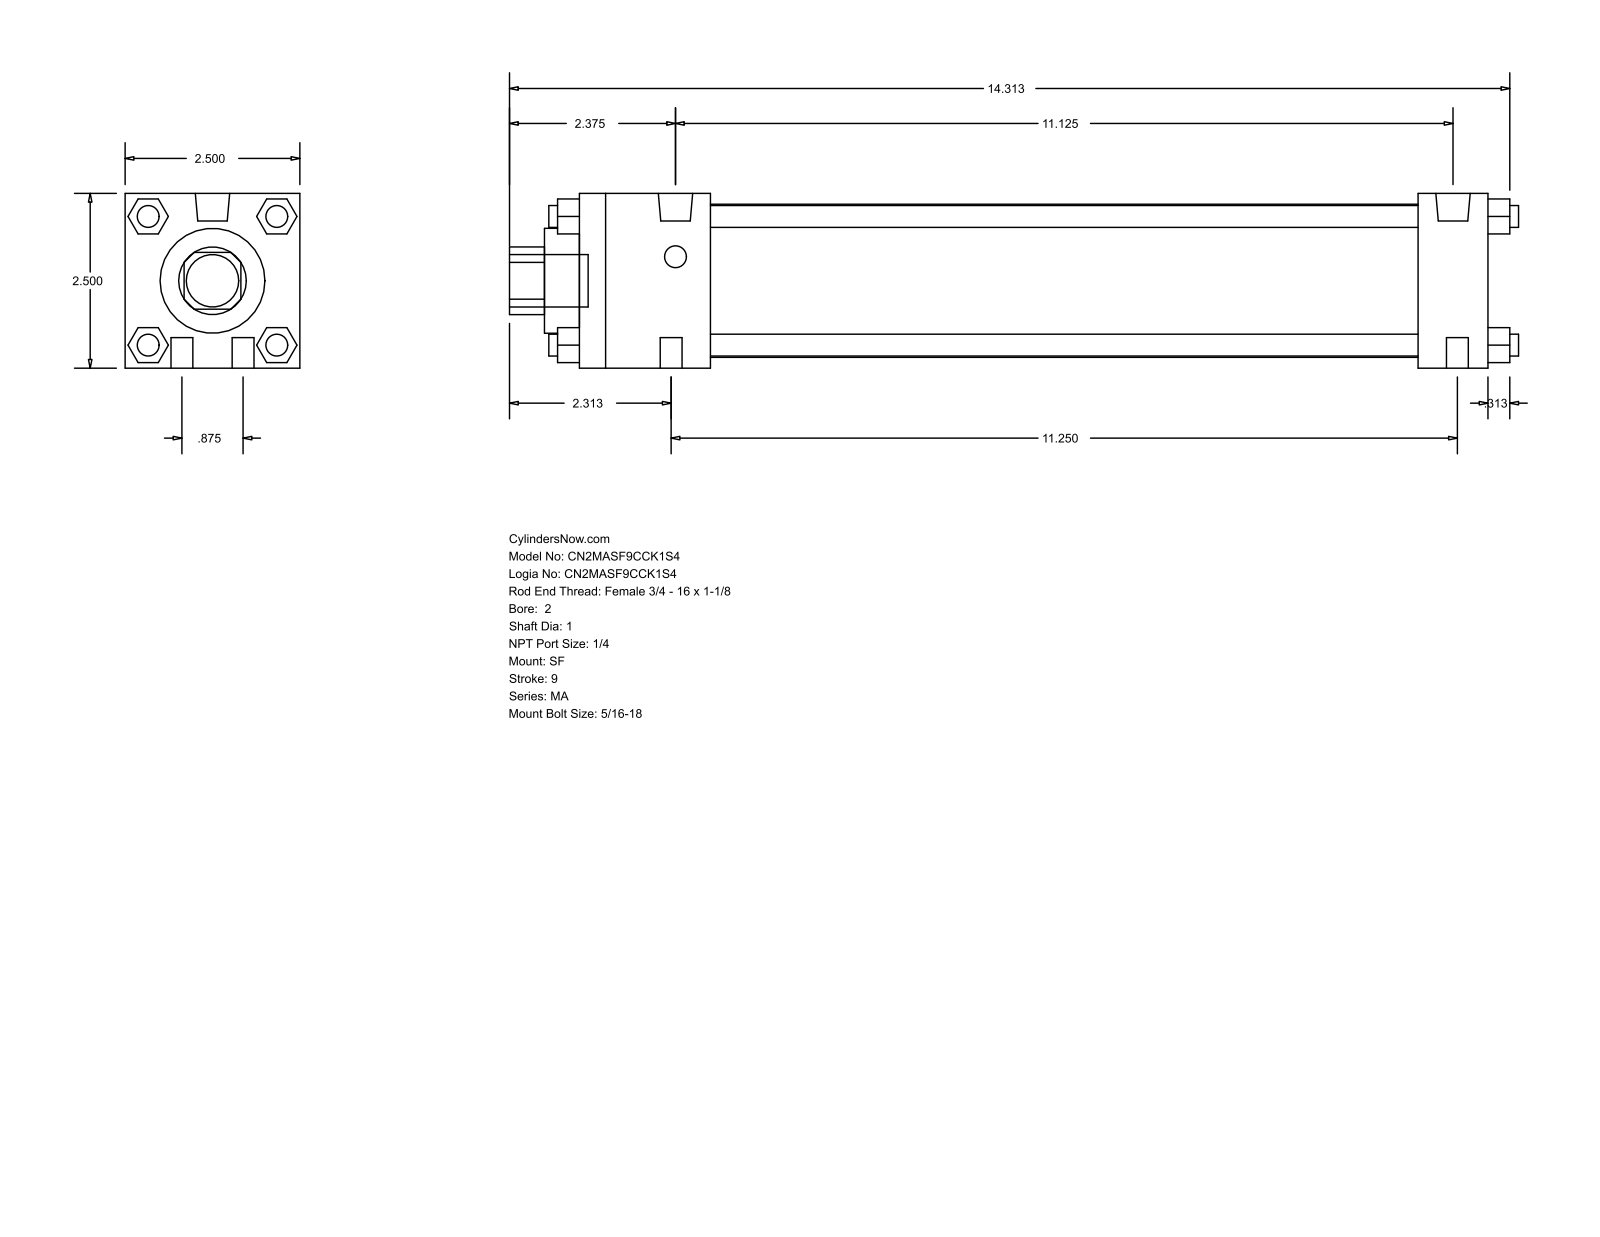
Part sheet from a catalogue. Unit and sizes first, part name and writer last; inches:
Units: inches
Overall size (bounding box): 14.437 × 2.5 × 2.5
Round holes (diameter × count): ⌀1 ×1, ⌀1.5 ×1, ⌀2.19 ×1
Round bosses / shafts (diameter × count): ⌀0.313 ×10, ⌀0.492 ×2, ⌀0.75 ×1
Partial cylindrical surfaces — rounded edges, fillets, slot ends (radius × count): R0.484 ×1
Main face-to-face distances: 2.5, 13, 0.5, 1, 12, 1.875, 10.125, 11.125, 1.593, 0.92
Bodies: 0 solids, 124 faces (94 planar, 30 cylindrical, 0 other)
Part name (STEP PRODUCT): MA_SF__0200_1
STEP written by: GSSL Pune (CONFIG_CONTROL_DESIGN)
